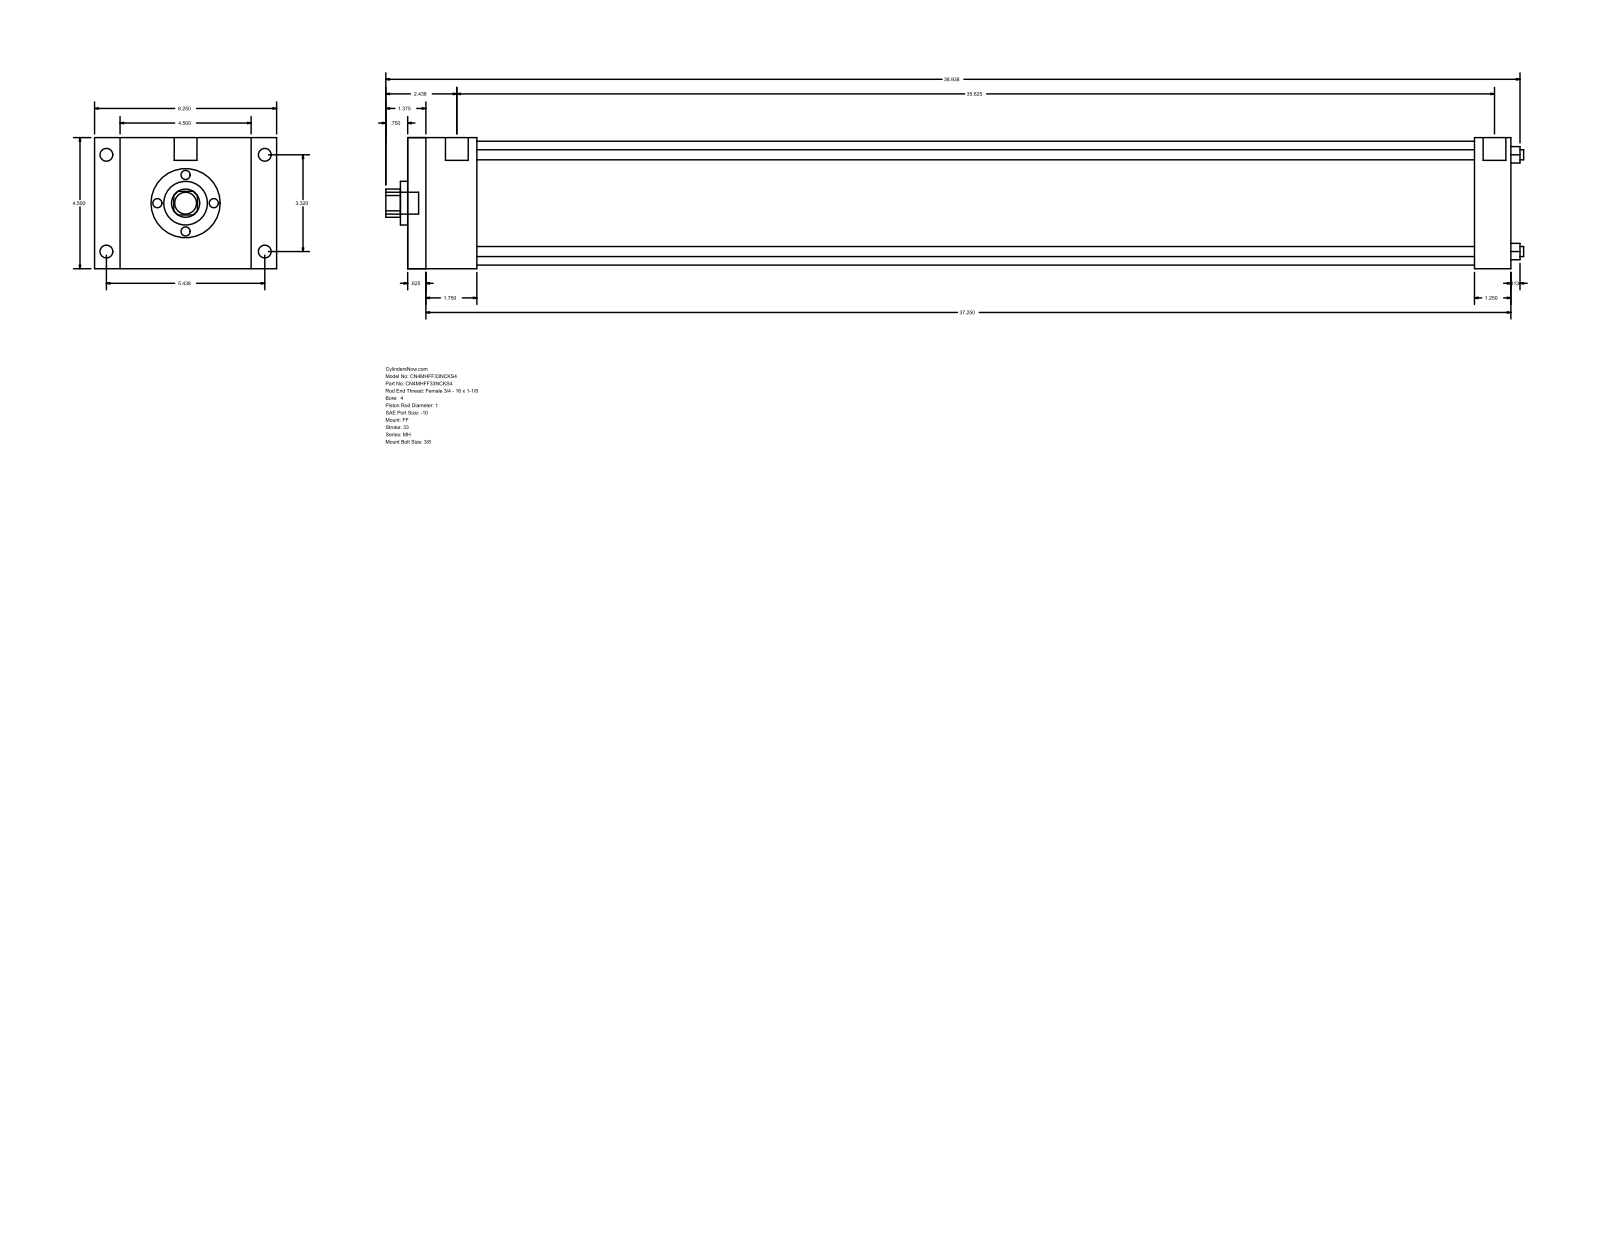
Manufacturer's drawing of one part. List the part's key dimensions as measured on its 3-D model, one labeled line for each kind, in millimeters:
Part name (STEP PRODUCT): MH_FF__0400_1
STEP written by: GSSL Pune (CONFIG_CONTROL_DESIGN)
Units: millimetres
Bodies: 0 solids, 92 faces (64 planar, 28 cylindrical, 0 other)
Overall size (bounding box): 992.19 × 158.75 × 114.3
Round holes (diameter × count): ⌀8.76 ×4, ⌀25.4 ×1, ⌀38.1 ×1, ⌀107.95 ×1
Round bosses / shafts (diameter × count): ⌀11.13 ×4, ⌀8.73 ×4, ⌀19.84 ×2, ⌀19.05 ×1
Partial cylindrical surfaces — rounded edges, fillets, slot ends (radius × count): R12.29 ×1
Main face-to-face distances: 114.3, 962.03, 15.87, 946.16, 60.33, 44.46, 901.7, 930.28, 914.41, 869.95
Hole centre spacings: 59.62, 84.32, 119.25
